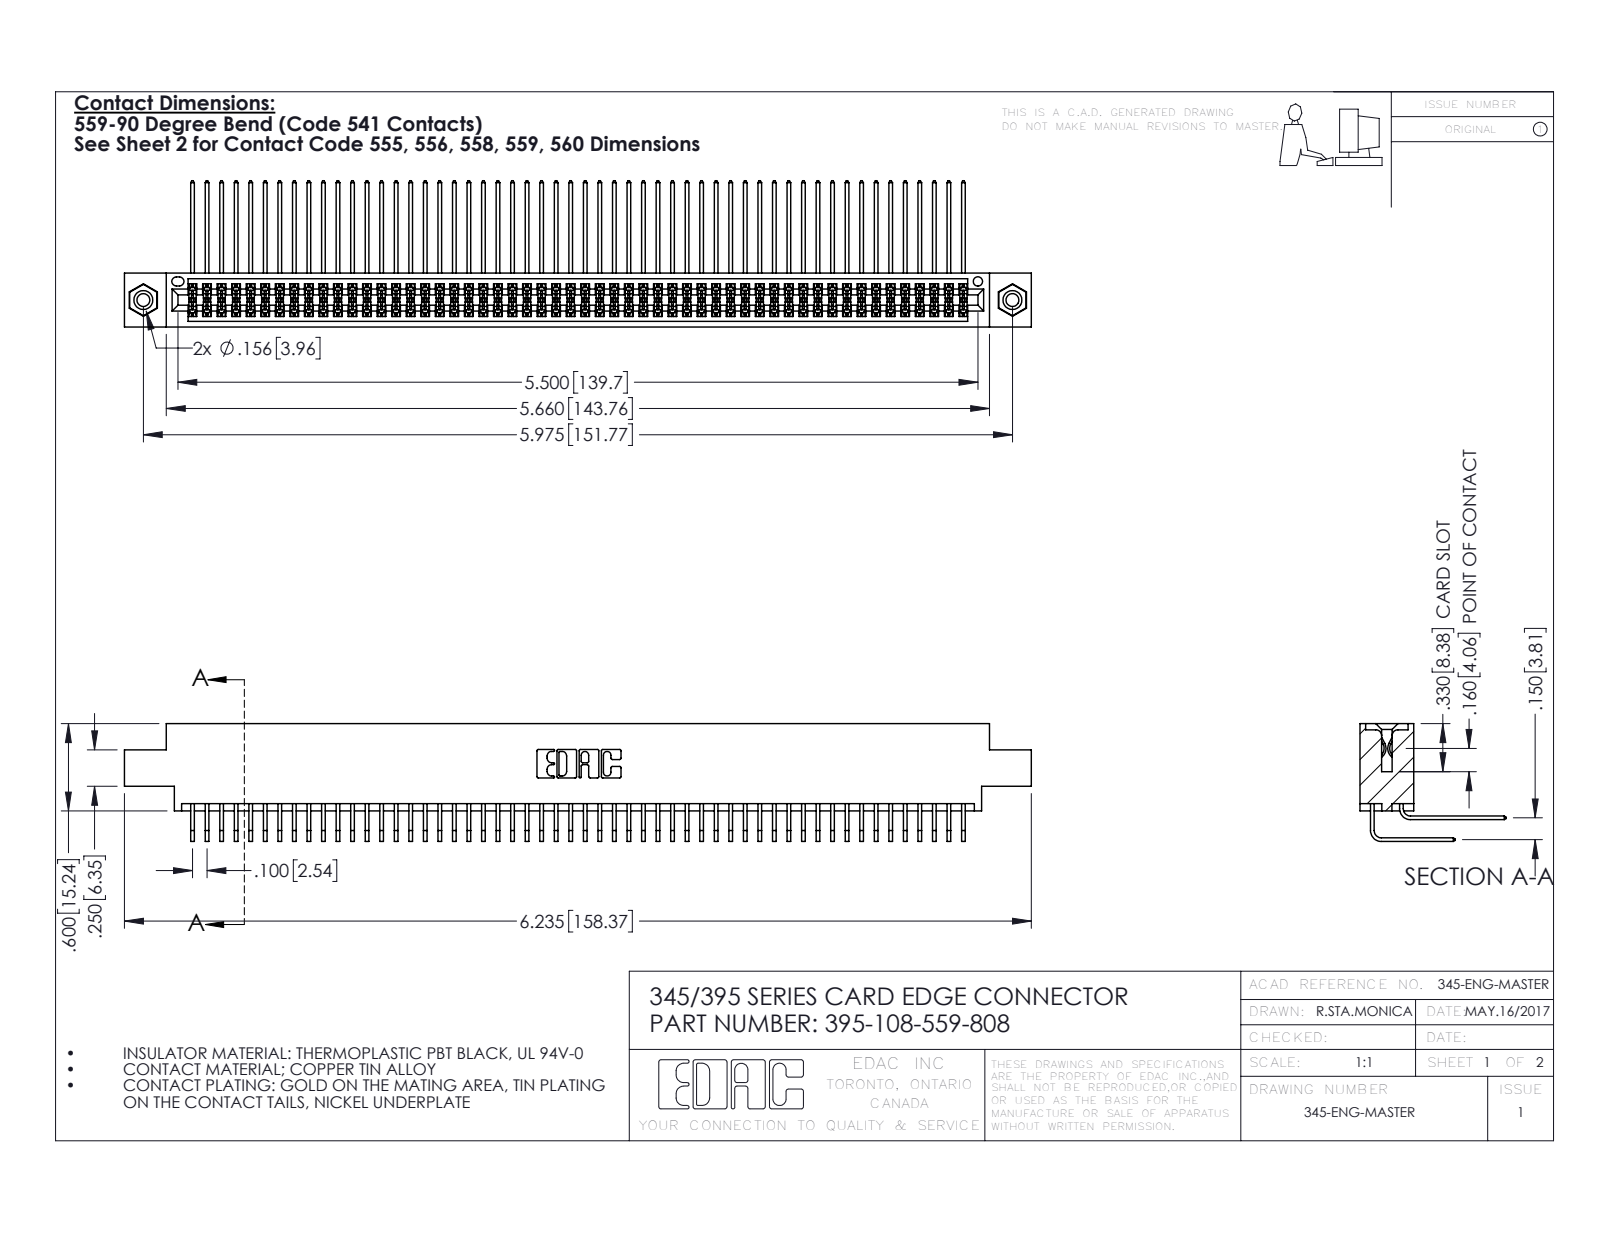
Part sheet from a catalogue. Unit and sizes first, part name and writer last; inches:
Units: inches
Overall size (bounding box): 6.235 × 1.005 × 0.809
Round holes (diameter × count): ⌀0.089 ×2, ⌀0.125 ×2, ⌀0.156 ×2, ⌀0.064 ×1
Round bosses / shafts (diameter × count): ⌀0.155 ×2
Partial cylindrical surfaces — rounded edges, fillets, slot ends (radius × count): R0.006 ×162, R0.01 ×22, R0.007 ×6, R0.031 ×6, R0.026 ×3, R0.014 ×2, R0.019 ×2, R0.022 ×2
Main face-to-face distances: 0.072, 0.298, 0.37, 0.2, 0.098, 0.272, 0.025, 0.225, 0.175, 0.15
Hole centre spacings: 0.27, 5.739, 5.975
Volume: 0.976 in³ · Surface area: 41.8 in²
Bodies: 111 solids, 5806 faces (3896 planar, 1894 cylindrical, 16 other)
Part name (STEP PRODUCT): 345-292-001_559 Tail - 2; 395-108-559-808; 345 Part_0.170 Offset - 0.156 Dia-TI; 345-292-001_558 559 Tail - 1 (+1 more)
STEP written by: SolidWorks 2016 (CONFIG_CONTROL_DESIGN)
